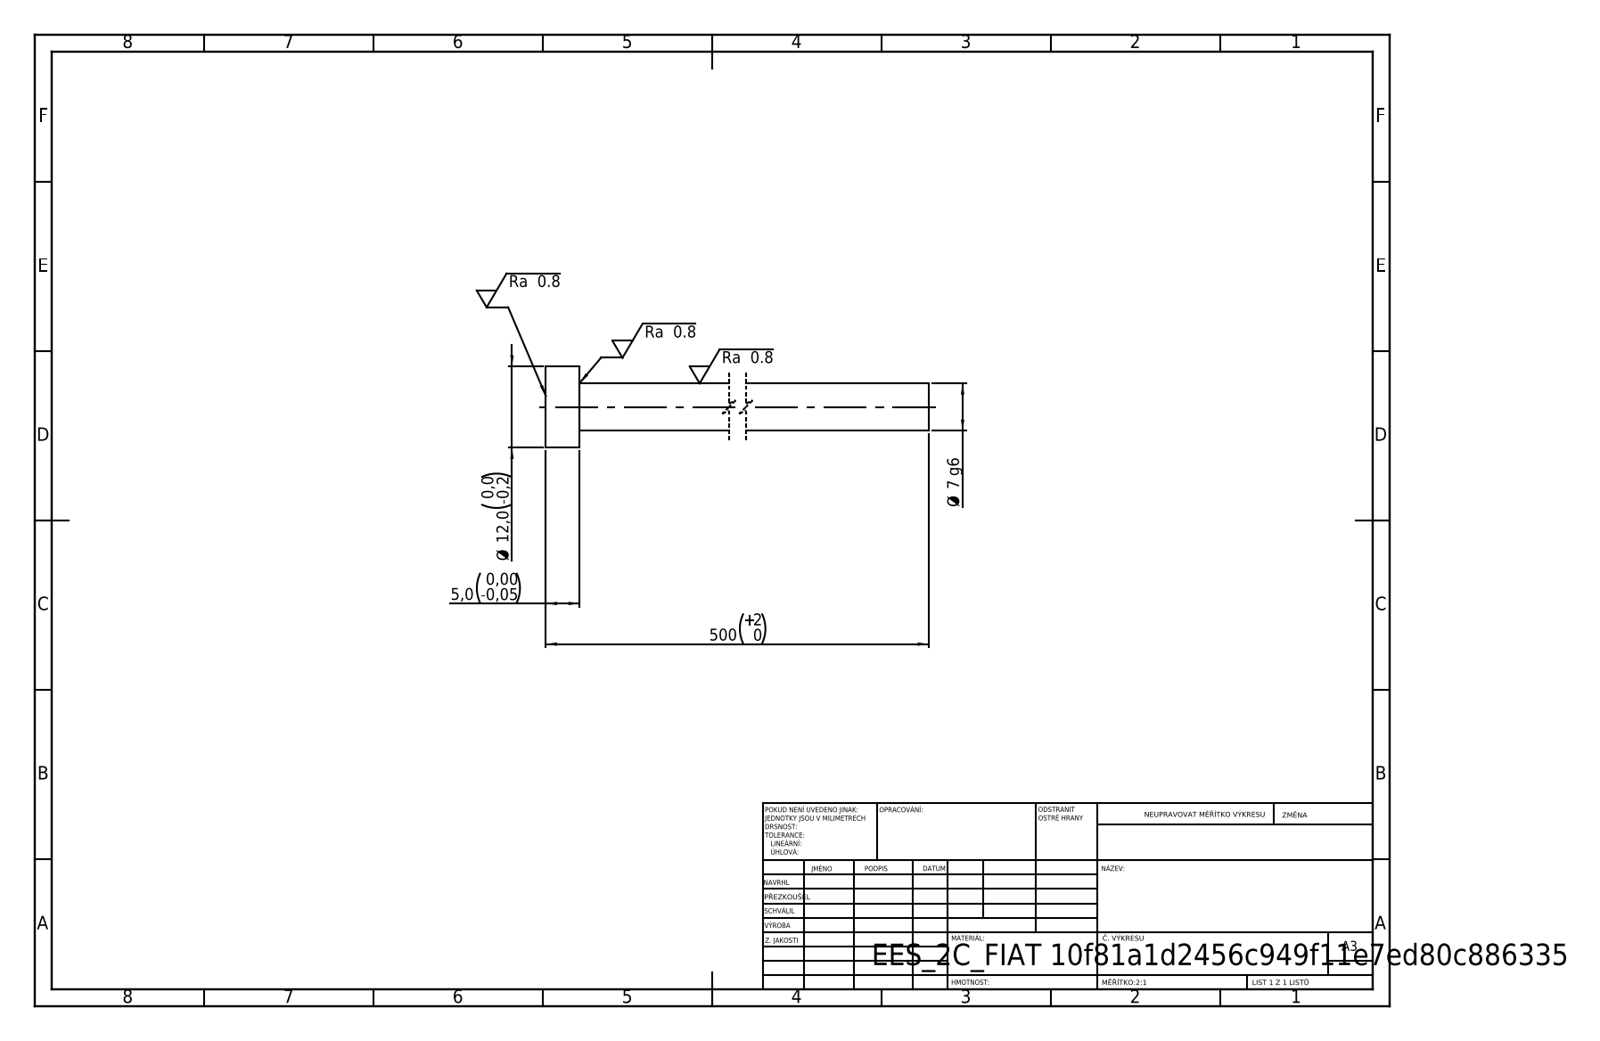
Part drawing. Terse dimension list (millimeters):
written by: SolidWorks 2019 (CONFIG_CONTROL_DESIGN)
unit: mm
bodies: 1 solid, 7 faces (3 planar, 4 cylindrical, 0 other)
size: 500 × 12 × 12
volume: 19 615 mm³; area: 11 300 mm²
bosses: 1× ⌀12, 1× ⌀7
face distances: 5, 500, 495
